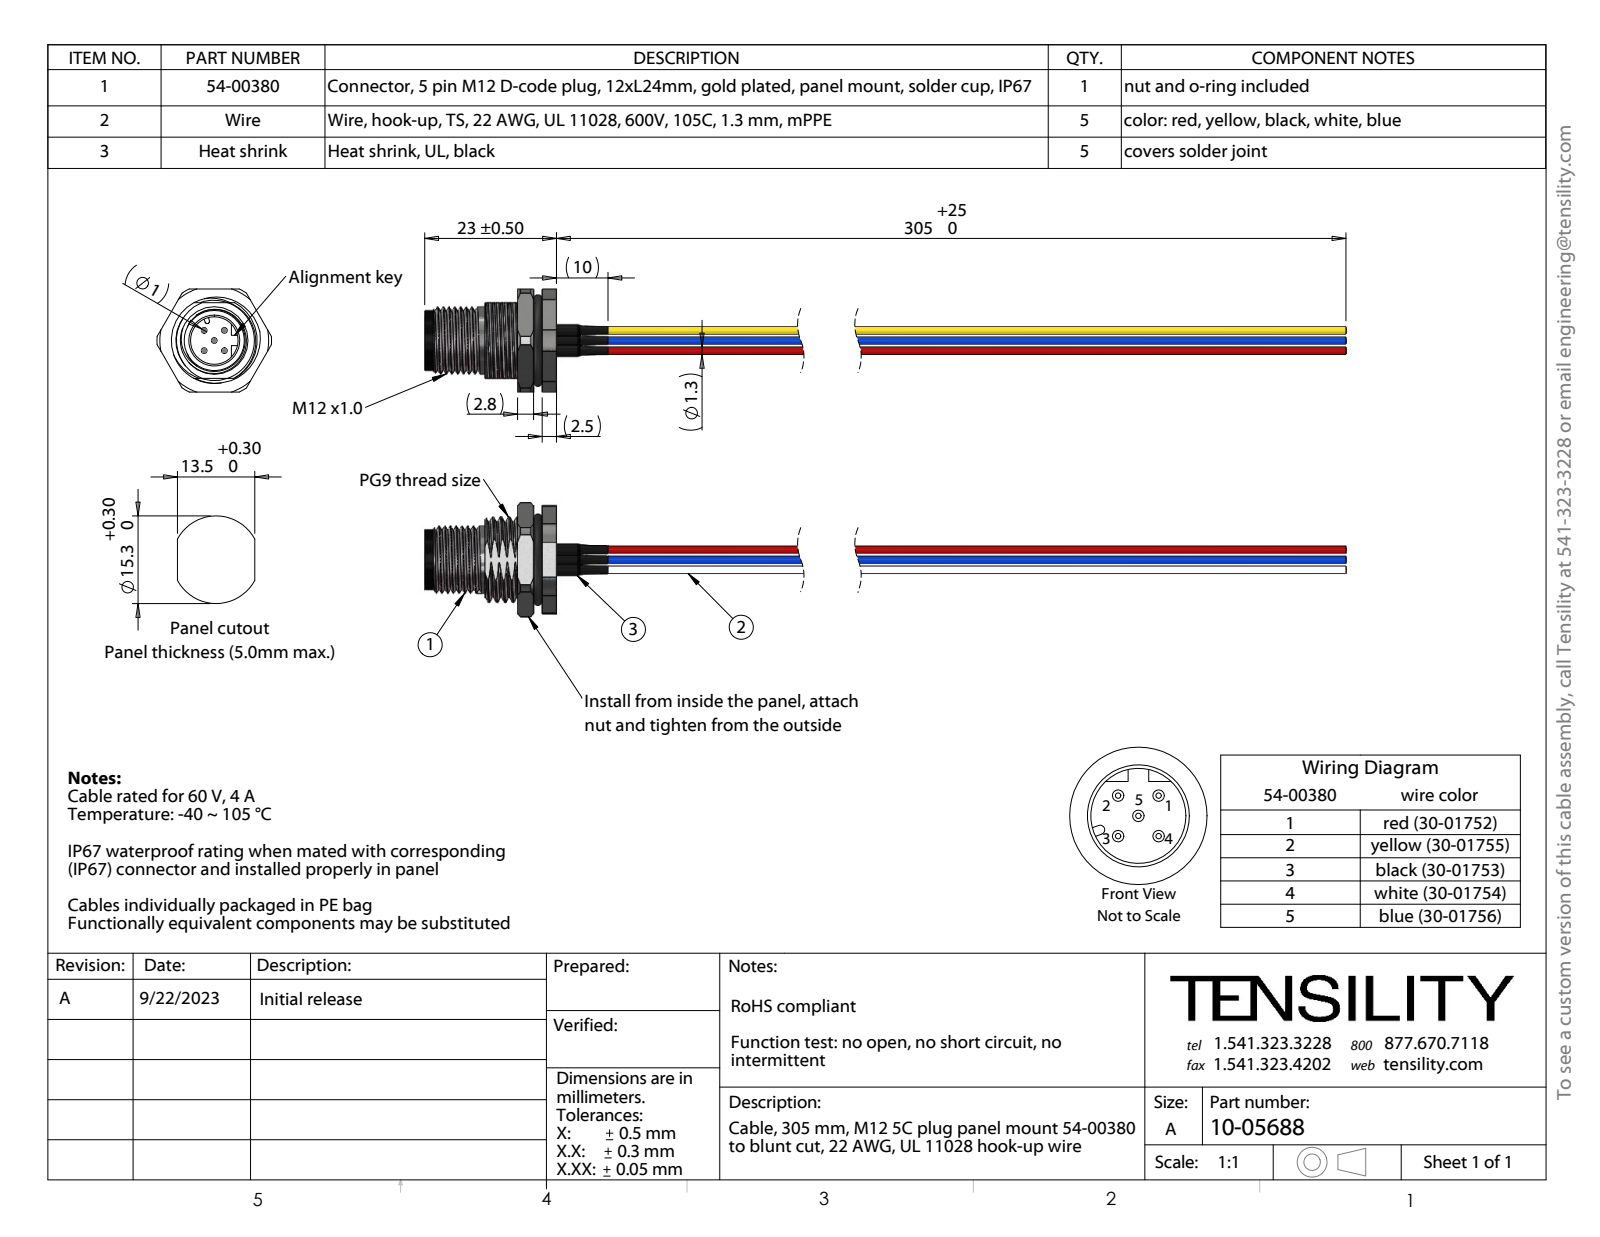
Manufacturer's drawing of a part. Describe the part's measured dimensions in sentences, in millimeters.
The part is named "Heat shrink; 30-01753_blunt cut; 30-01752_blunt cut; 54-00380-04 (+8 more)". Its 3-D file was written by "SolidWorks 2021 (CONFIG_CONTROL_DESIGN)". It is 105 solids with 955 faces: 269 planar, 522 cylindrical and 164 other. Overall it measures 174.3 by 20 by 18 millimeters. Its volume is 4 155 cubic millimeters and its surface area 21 867 square millimeters. Round holes: 5 of diameter 0.8, 5 of diameter 1, 1 of diameter 8, 1 of diameter 8.3, 1 of diameter 9.2, 1 of diameter 11, 1 of diameter 14. Round bosses or shafts: 5 of diameter 2, 5 of diameter 1.4, 5 of diameter 1.3, 1 of diameter 13.2, 1 of diameter 12, 1 of diameter 11.8, 1 of diameter 10.5, 1 of diameter 9. Partial cylindrical surfaces (rounded edges, fillets, slot ends): 3 of radius 2.41, 1 of radius 0.4, 1 of radius 7.5, 1 of radius 9.5, 1 of radius 10. The main face-to-face distances are 1.5, 7.5, 6.5, 4, 5, 3, 2.5, 3.5, 1, 18. The hole center spacings are 0.32, 0.48, 0.31, 0.45, 0.53, 0.33, 5.38, 0.37.
